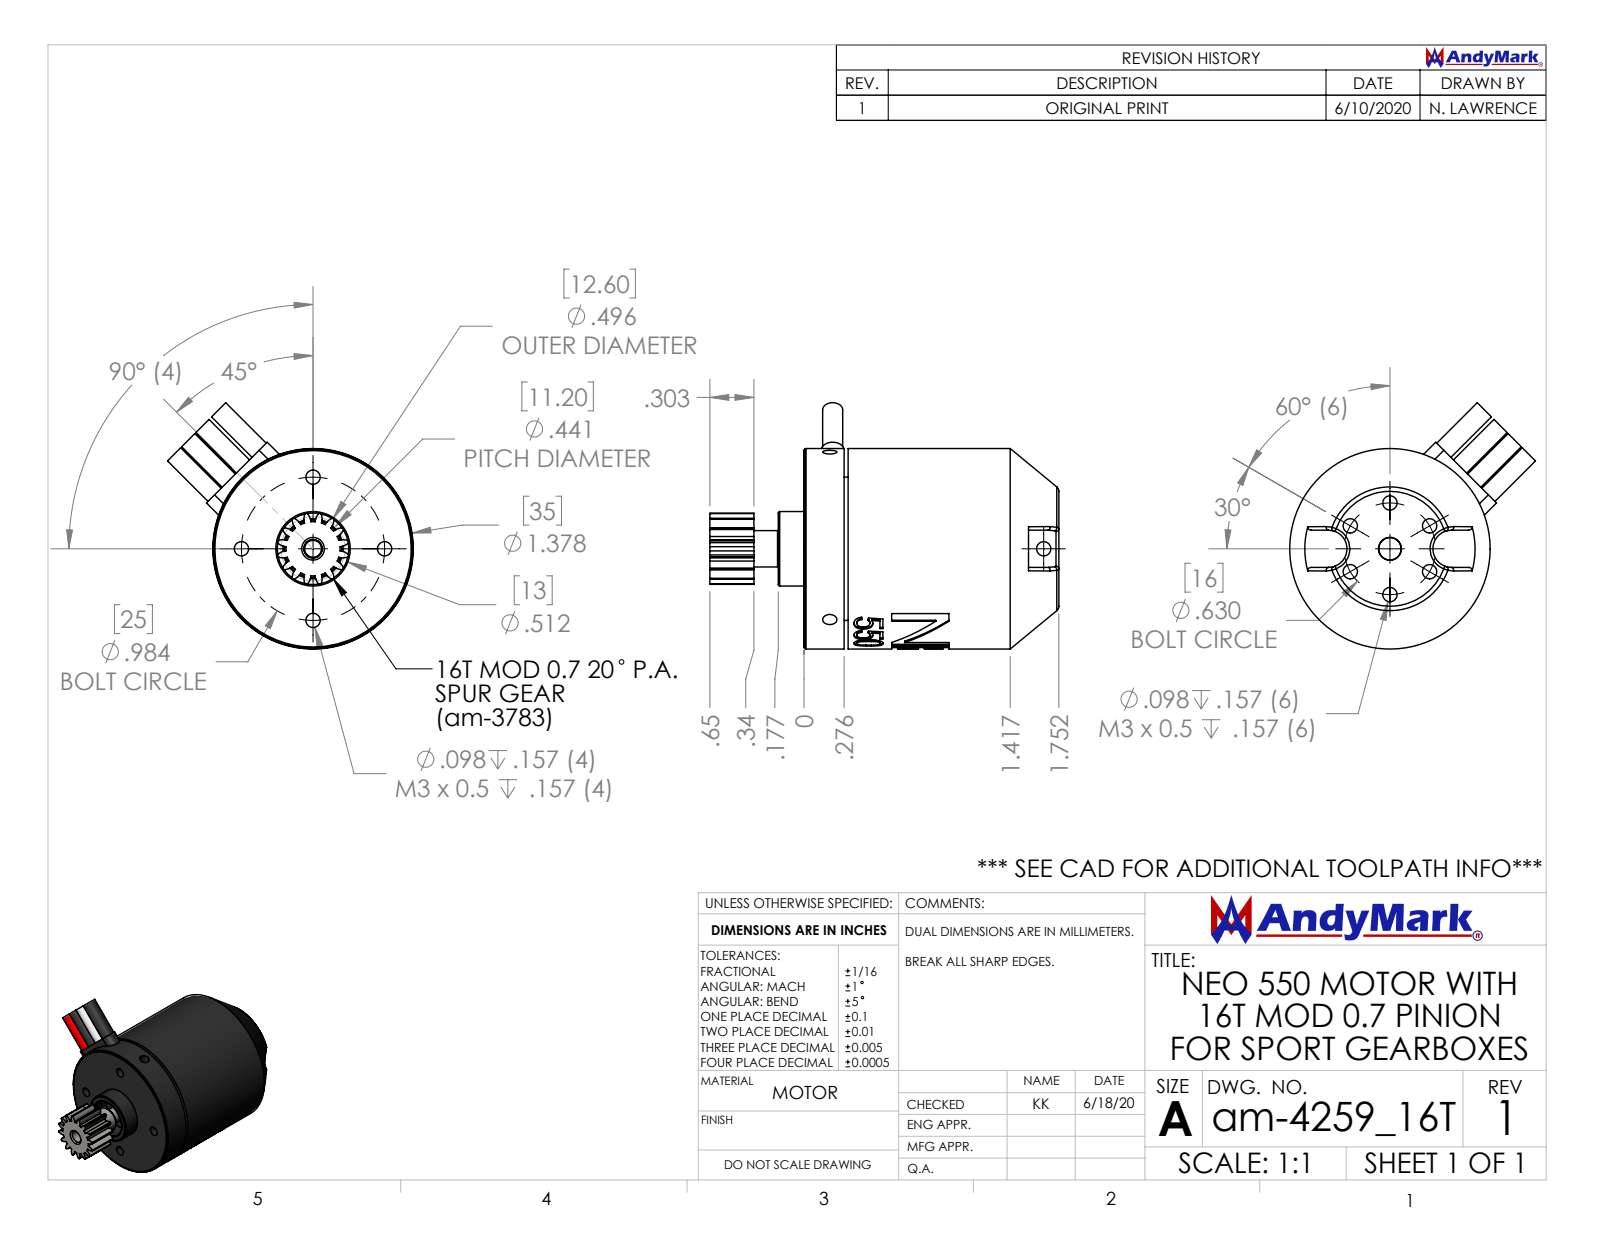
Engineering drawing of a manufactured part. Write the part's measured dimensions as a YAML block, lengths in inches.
part_name: "am-4259_16T NEO550 with 16T 0.7mod Pinion for Sport Gearboxes"
step_written_by: "SolidWorks 2019 (AUTOMOTIVE_DESIGN)"
units: inches
bodies: {solids: 2, faces: 247, planar: 64, cylindrical: 105, other: 78}
overall_size: [2.399, 1.693, 1.689]
volume: 2.472
surface_area: 15.02
round_holes:
  - {diameter: 0.098, count: 14}
  - {diameter: 0.126, count: 1}
  - {diameter: 0.157, count: 1}
  - {diameter: 0.394, count: 1}
round_bosses_or_shafts:
  - {diameter: 0.128, count: 3}
  - {diameter: 1.378, count: 1}
  - {diameter: 0.984, count: 1}
  - {diameter: 0.512, count: 1}
  - {diameter: 0.25, count: 1}
  - {diameter: 0.154, count: 1}
  - {diameter: 0.138, count: 1}
  - {diameter: 0.125, count: 1}
partial_cylinders:
  - {radius: 0.088, count: 32}
  - {radius: 0.079, count: 2}
  - {radius: 0.128, count: 2}
  - {radius: 0.186, count: 1}
  - {radius: 0.248, count: 1}
  - {radius: 0.679, count: 1}
face_to_face_distances: [0.276, 0.028, 0.303, 1.449, 1.476, 1.752, 0.209, 1.24, 1.268, 1.543]
hole_center_spacings: [0.315, 0.546, 0.27, 0.432, 0.492, 0.584, 0.696, 0.705]
